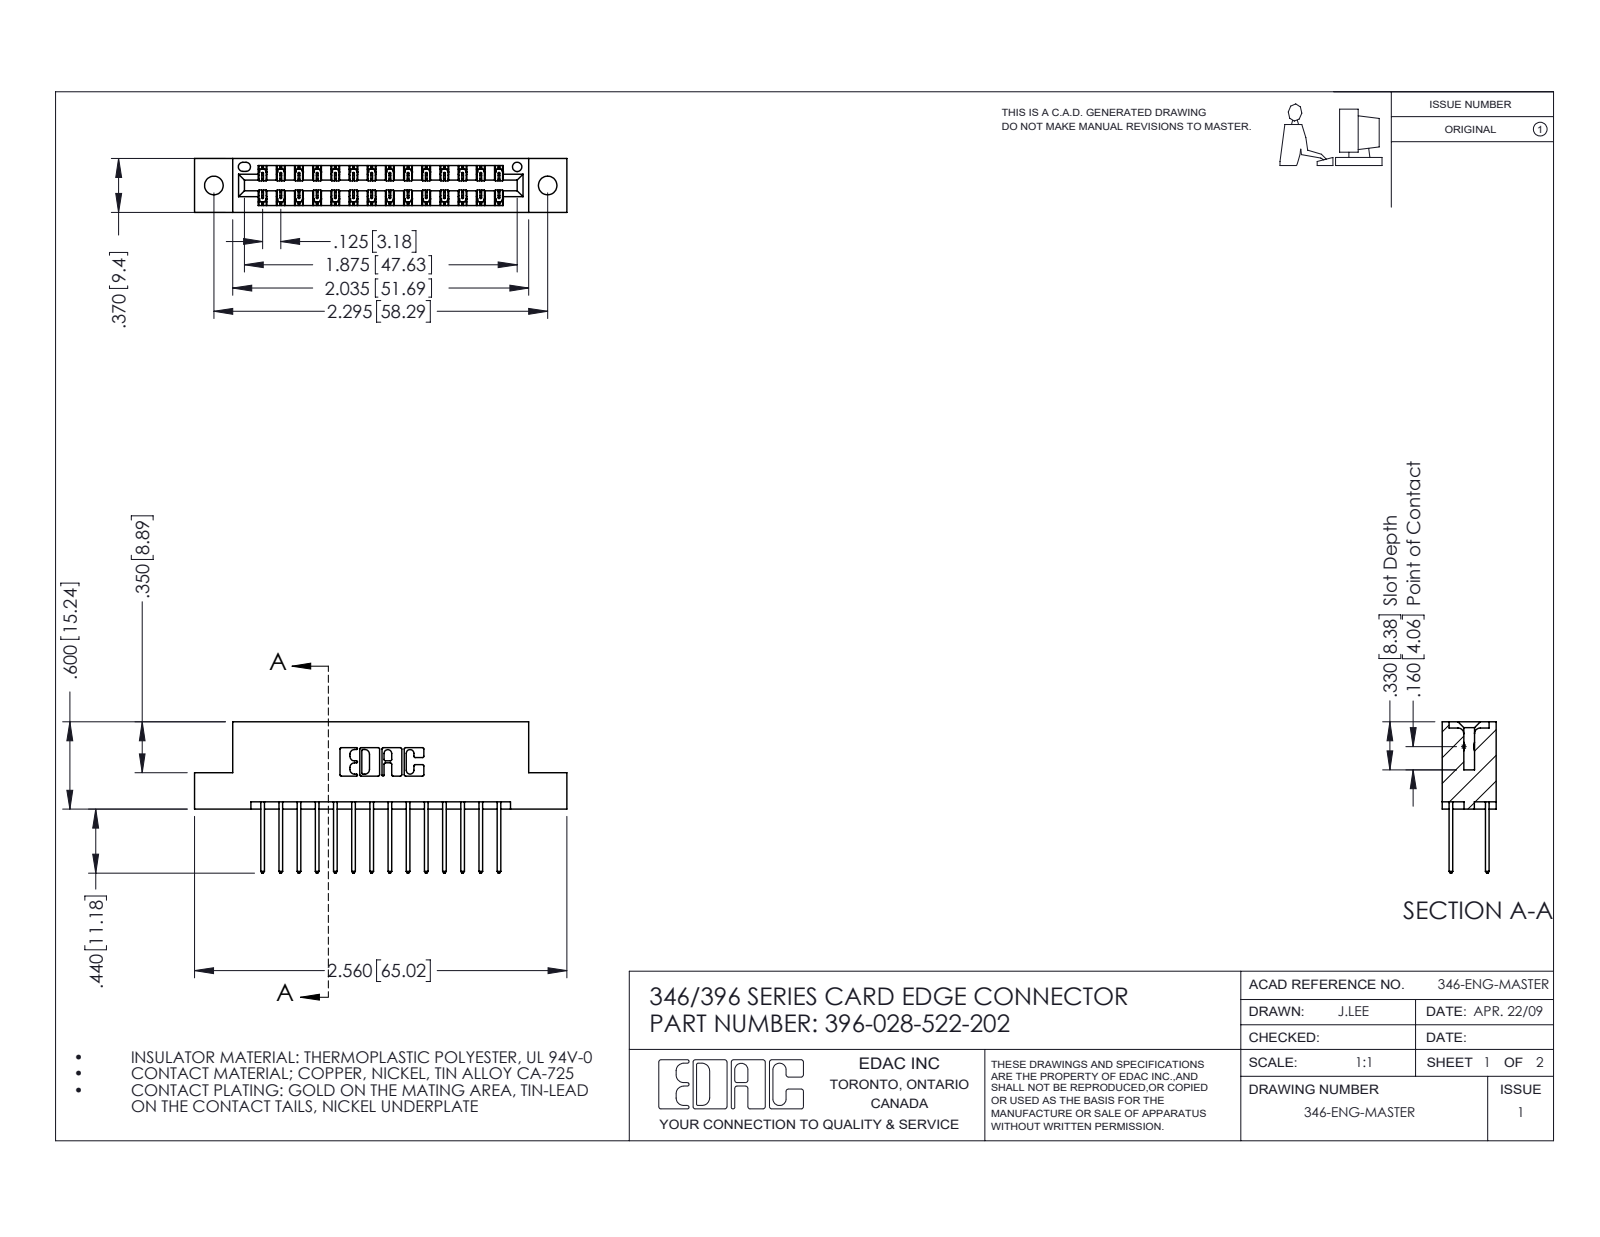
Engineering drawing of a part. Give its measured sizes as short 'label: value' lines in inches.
name: 396-028-522-202; 345-292-001_345-293-122; 346 Part_Flush Mounting Lugs - 0.128 Dia
written by: SolidWorks 2016 (CONFIG_CONTROL_DESIGN)
unit: in
bodies: 29 solids, 1578 faces (1056 planar, 522 cylindrical, 0 other)
size: 2.56 × 1.04 × 0.37
volume: 0.376 in³; area: 12.54 in²
holes: 2× ⌀0.128, 1× ⌀0.064
rounds: 42× R0.006, 28× R0.01, 22× R0.01, 6× R0.007, 6× R0.031, 3× R0.026, 2× R0.014, 2× R0.022
face distances: 0.25, 0.048, 0.322, 0.37, 0.072, 0.298, 0.025, 0.275, 0.148, 0.222
hole spacings: 0.246, 2.089, 2.295
